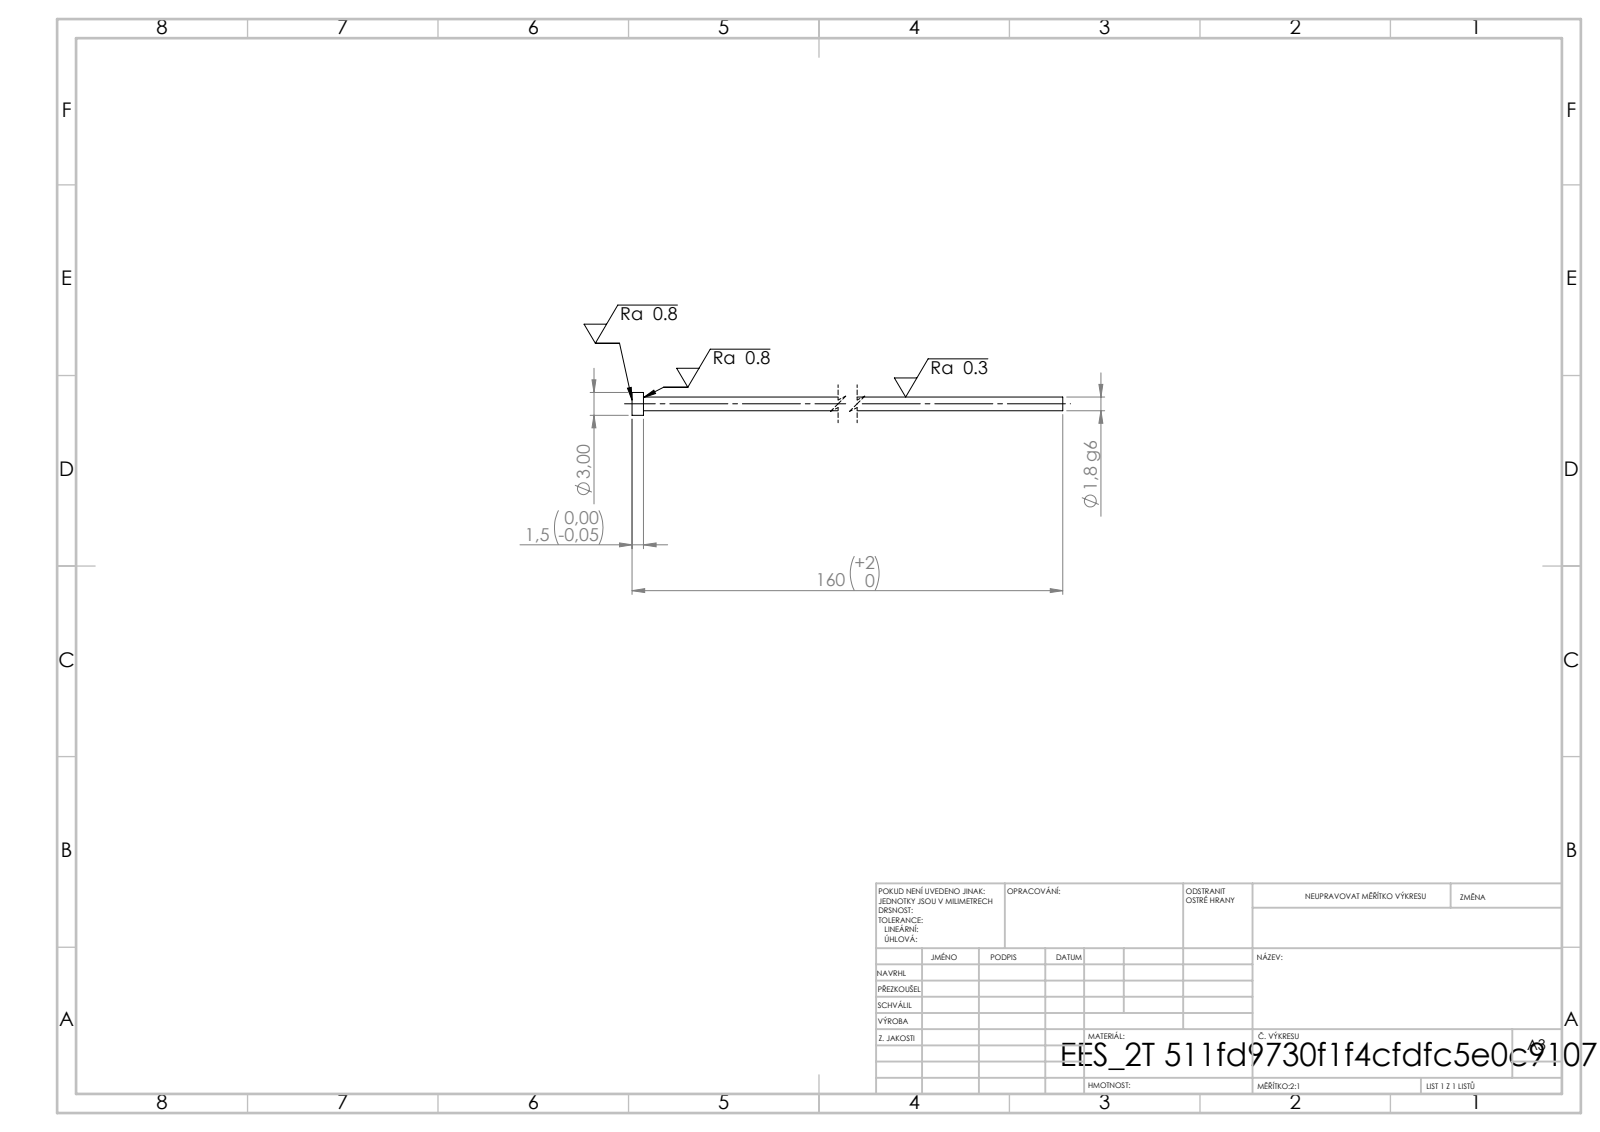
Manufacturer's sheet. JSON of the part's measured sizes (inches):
{"step_written_by": "SolidWorks 2019 (CONFIG_CONTROL_DESIGN)", "units": "inches", "bodies": {"solids": 1, "faces": 7, "planar": 3, "cylindrical": 4, "other": 0}, "overall_size": [6.299, 0.118, 0.118], "volume_in3": 0.025, "surface_area_in2": 1.43, "round_bosses_or_shafts": [[0.118, 1], [0.071, 1]], "face_to_face_distances": [0.059, 6.299, 6.24]}
